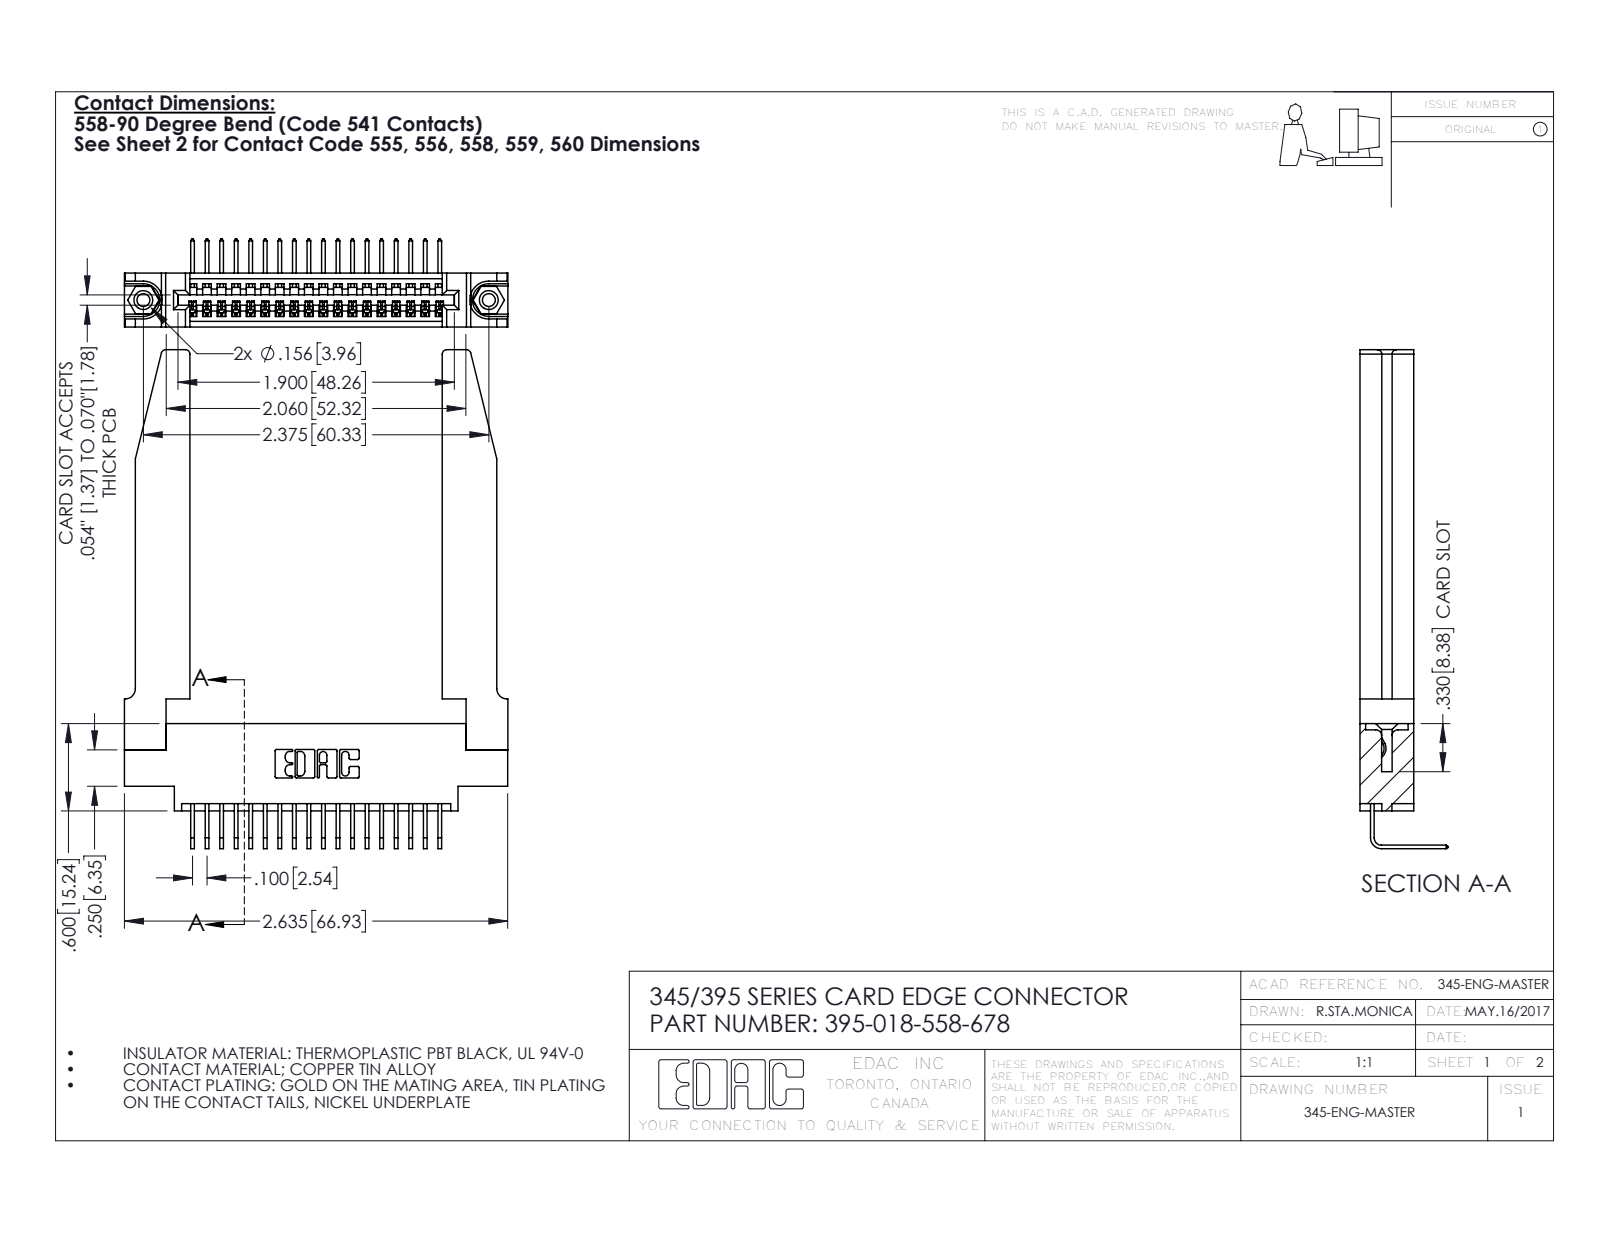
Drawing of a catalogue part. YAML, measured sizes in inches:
part_name: "395-018-558-678; 345-292-001_558 Tail - 2; 345-220-078_345-220-078; 345 Part_0.170 Offset - 0.156 Dia-TH (+1 more)"
step_written_by: "SolidWorks 2016 (CONFIG_CONTROL_DESIGN)"
units: inches
bodies: {solids: 23, faces: 1444, planar: 982, cylindrical: 410, other: 52}
overall_size: [3.429, 2.636, 0.605]
volume: 0.847
surface_area: 23.43
round_holes:
  - {diameter: 0.089, count: 2}
  - {diameter: 0.125, count: 2}
  - {diameter: 0.156, count: 2}
  - {diameter: 0.064, count: 1}
round_bosses_or_shafts:
  - {diameter: 0.155, count: 2}
partial_cylinders:
  - {radius: 0.006, count: 36}
  - {radius: 0.01, count: 22}
  - {radius: 0.03, count: 8}
  - {radius: 0.007, count: 6}
  - {radius: 0.031, count: 6}
  - {radius: 0.026, count: 3}
  - {radius: 0.031, count: 2}
  - {radius: 0.04, count: 2}
face_to_face_distances: [0.37, 0.072, 0.298, 0.15, 0.148, 0.098, 0.272, 0.025, 0.2, 0.22]
hole_center_spacings: [0.27, 2.141, 2.375]
